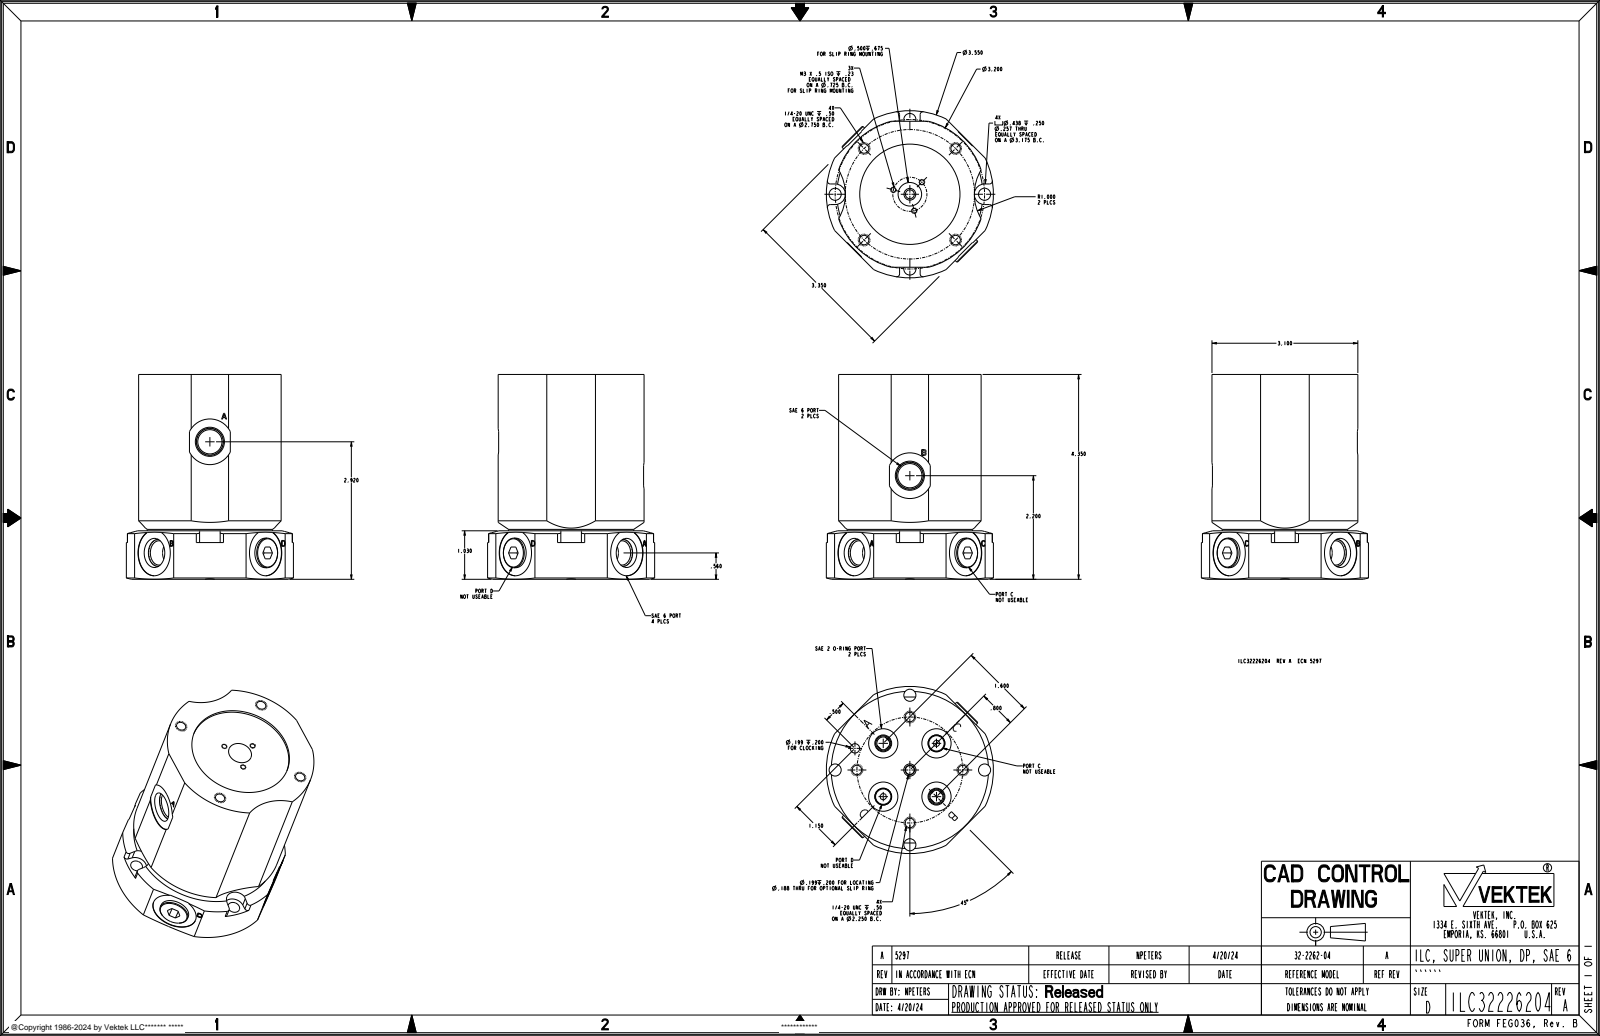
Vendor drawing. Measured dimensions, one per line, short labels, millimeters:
name: ILC32226204
written by: CREO PARAMETRIC BY PTC INC, 2021164 (AUTOMOTIVE_DESIGN)
unit: mm
bodies: 1 solid, 526 faces (278 planar, 156 cylindrical, 92 other)
size: 110.5 × 88.1 × 85.1
volume: 543 600 mm³; area: 60 780 mm²
holes: 11× ⌀6.4, 8× ⌀5.1, 4× ⌀6.5, 4× ⌀6.9, 4× ⌀15.8, 3× ⌀2.5, 3× ⌀3, 3× ⌀13.1, 2× ⌀5.1, 2× ⌀24.6, 1× ⌀4.8, 1× ⌀12.7
bosses: 4× ⌀14.3, 4× ⌀8, 2× ⌀9, 1× ⌀67.6, 1× ⌀16
rounds: 8× R1.5, 4× R5.6, 2× R12.3, 2× R25.4, 1× R40.6, 1× R45.1
face distances: 110.5, 109.1, 1.4, 78.7, 26.2, 82.9, 84.3, 84.8, 84.6, 85.1
hole spacings: 20.2, 25, 29.2, 29.7, 40.4, 45.3, 49.4, 56.5
